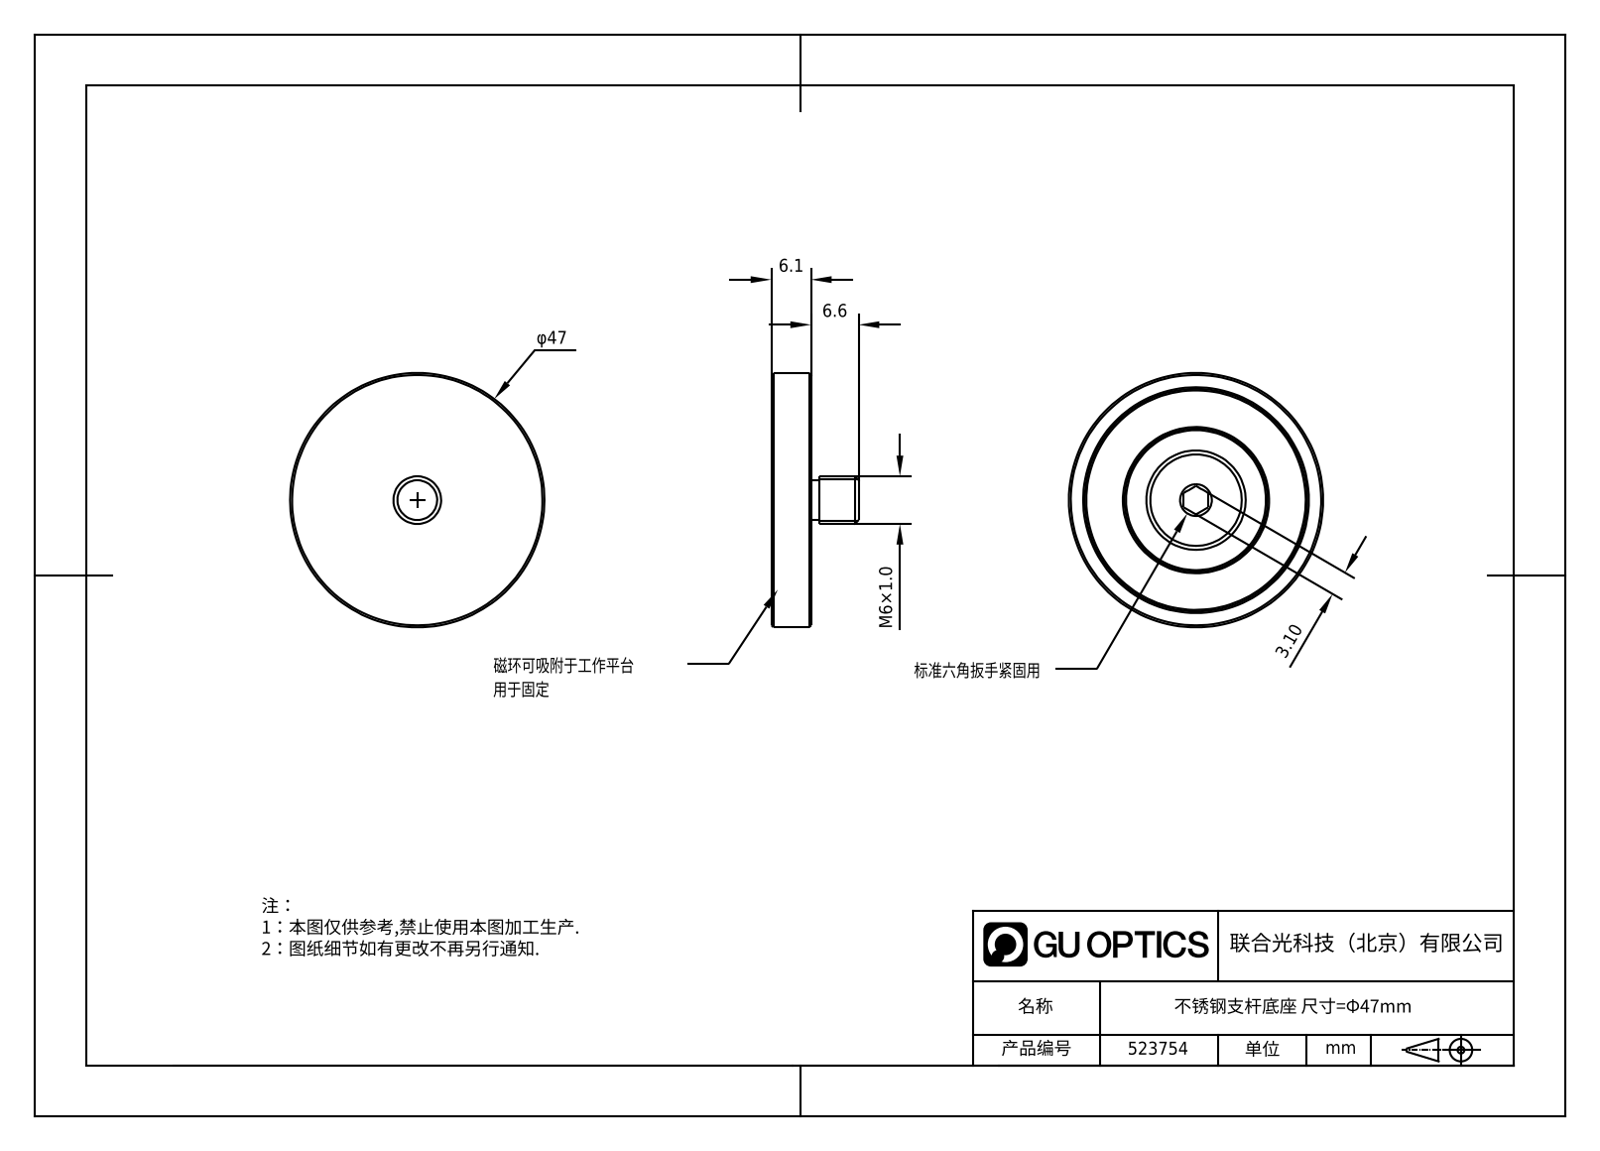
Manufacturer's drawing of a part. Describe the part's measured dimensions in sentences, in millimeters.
The part is named "1.4.6.3_ZGD-1.5B，1.5英寸支杆底座，带M6x6mm螺丝，A". Its 3-D file was written by "SolidWorks 2021 (CONFIG_CONTROL_DESIGN)". It is 1 solid with 28 faces: 12 planar, 6 cylindrical and 10 other. Overall it measures 47 by 47 by 12.7 millimeters. Its volume is 10 498 cubic millimeters and its surface area 4 506 square millimeters. Round bosses or shafts: 1 of diameter 47, 1 of diameter 6, 1 of diameter 5. The main face-to-face distances are 6.1, 5.6, 0.5, 6.6, 12.7, 12.2, 3.1, 7.1, 1, 3.5.
